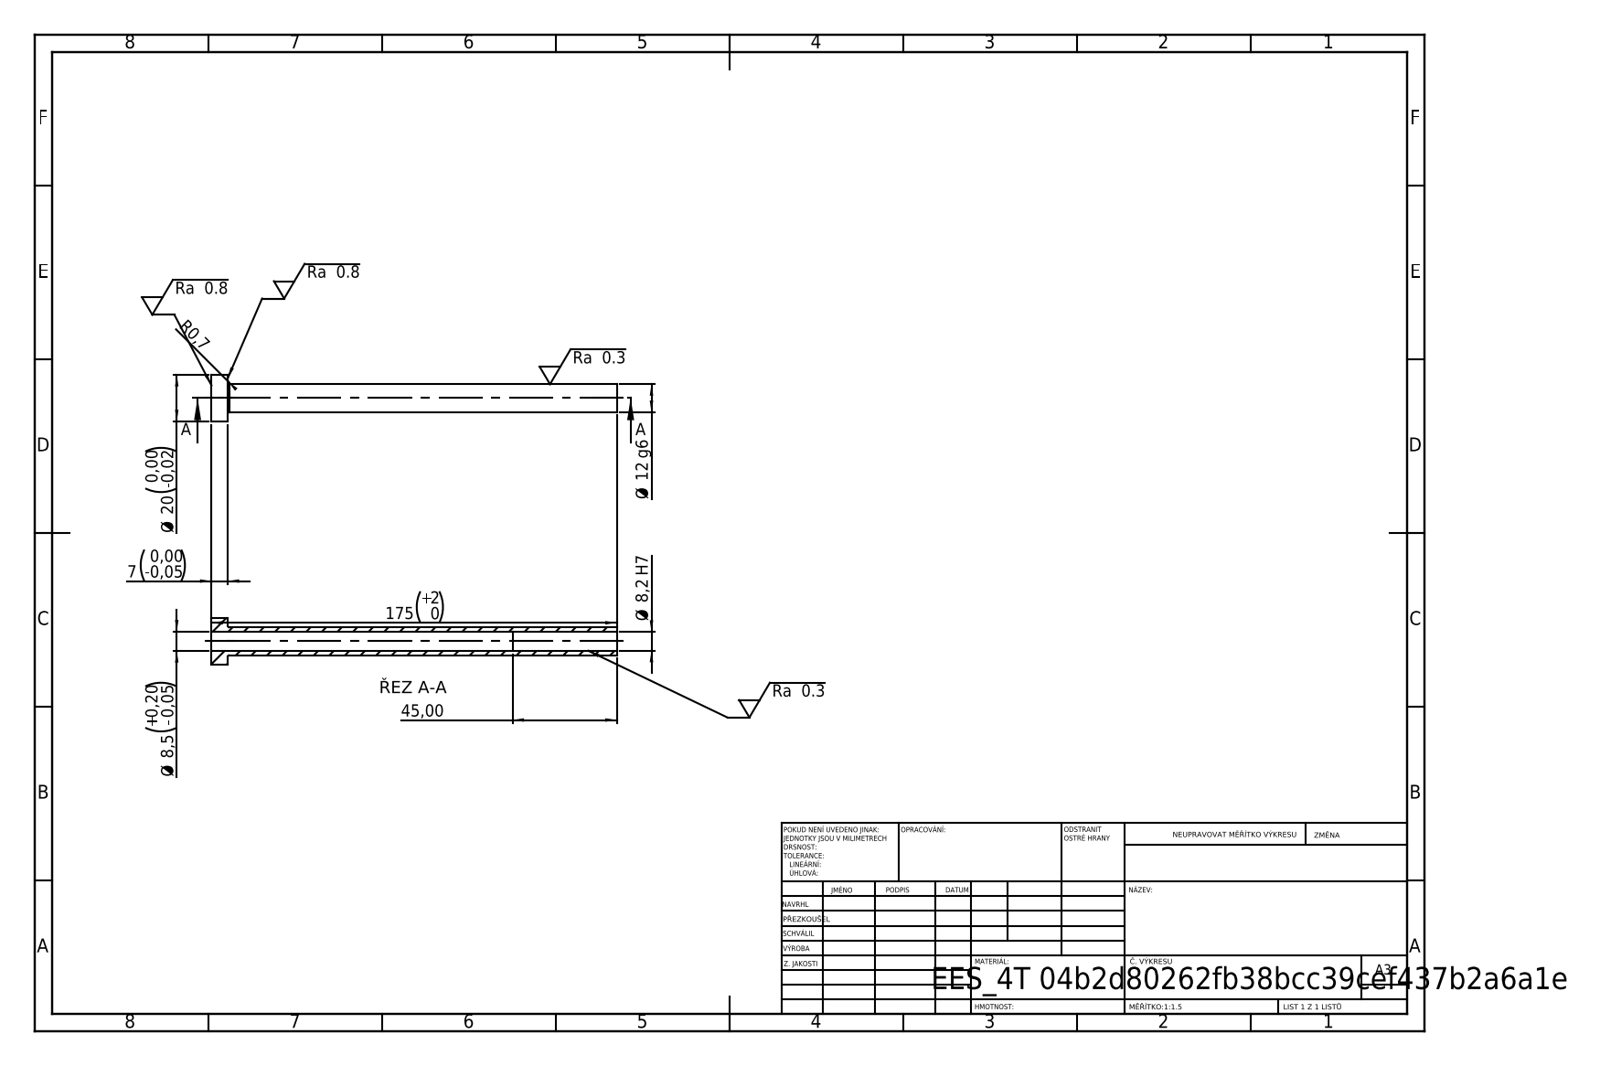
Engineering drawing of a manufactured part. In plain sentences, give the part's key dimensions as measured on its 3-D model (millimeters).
Its 3-D file was written by "SolidWorks 2019 (CONFIG_CONTROL_DESIGN)". It is 1 solid with 14 faces: 4 planar, 8 cylindrical and 2 other. Overall it measures 175 by 20 by 20 millimeters. Its volume is 11 450 cubic millimeters and its surface area 11 916 square millimeters. Round holes: 1 of diameter 8.2, 1 of diameter 8.5. Round bosses or shafts: 1 of diameter 20, 1 of diameter 12. The main face-to-face distances are 7, 175, 168, 130, 123, 45.
